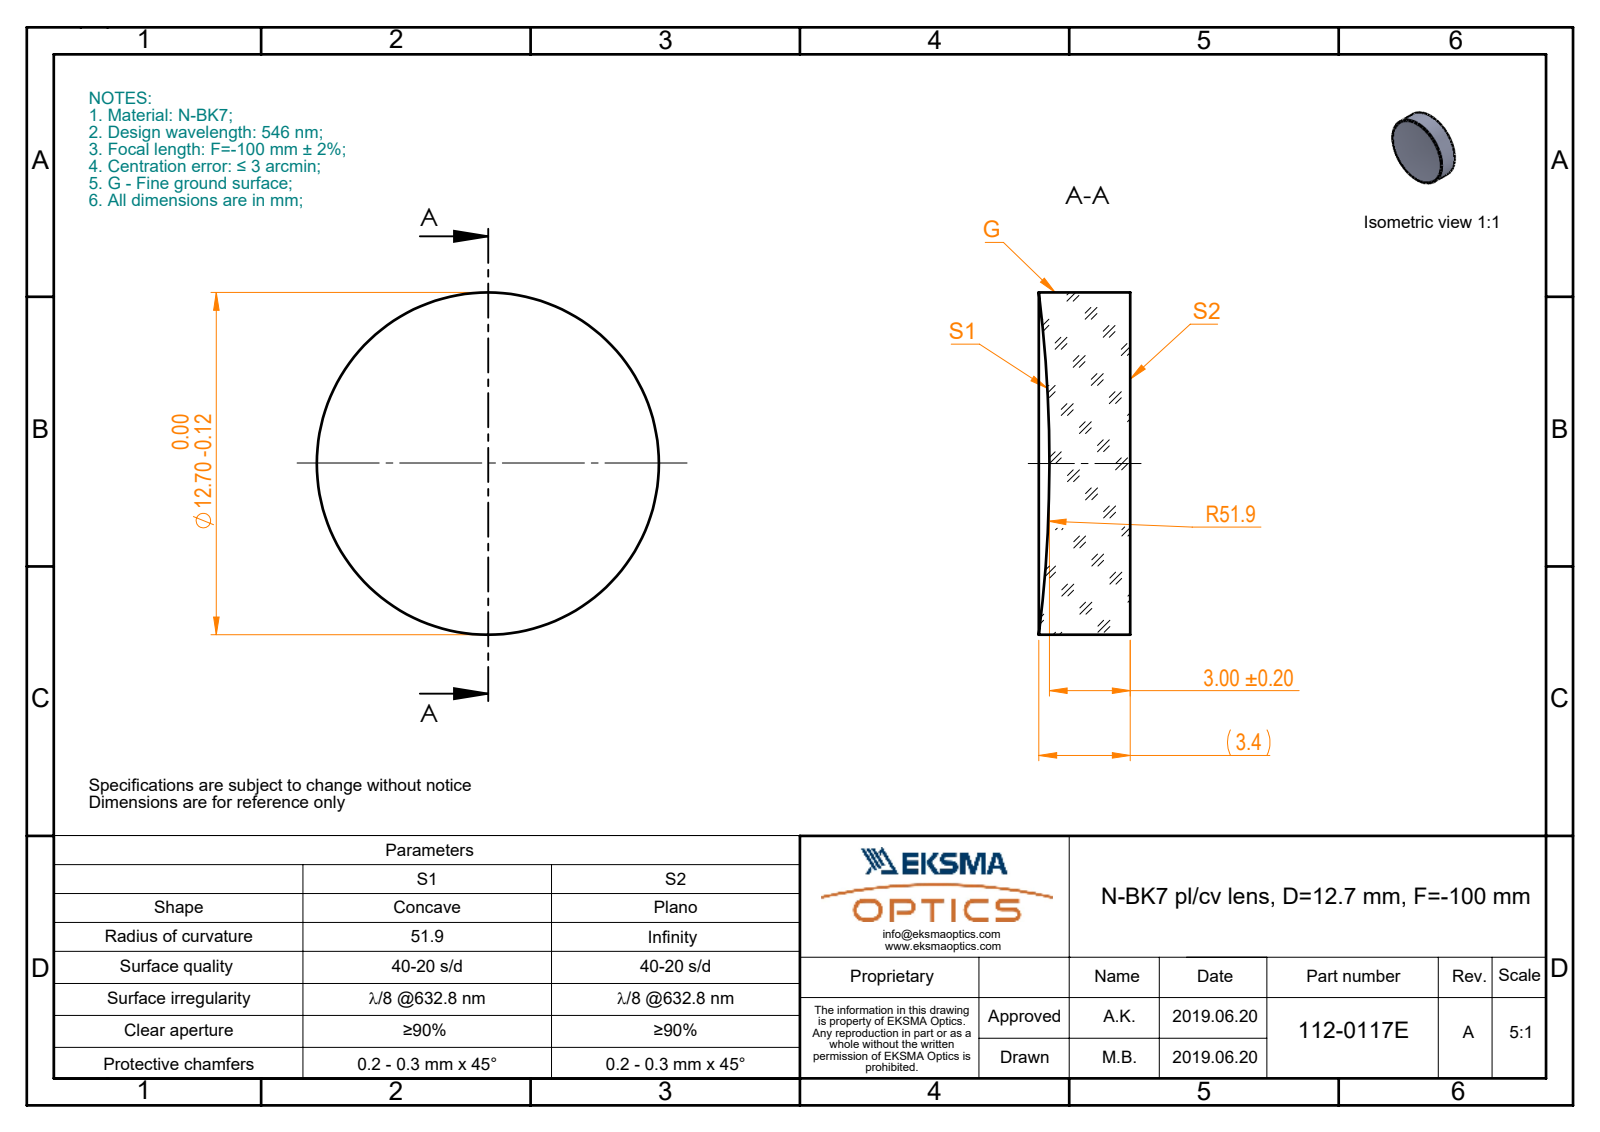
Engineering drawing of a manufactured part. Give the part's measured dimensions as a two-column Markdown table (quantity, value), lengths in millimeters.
| quantity | value |
| --- | --- |
| part name | 112-0117E BK7 pl-cv 12.7 F-100 |
| STEP written by | SolidWorks 2017 (CONFIG_CONTROL_DESIGN) |
| units | millimeters |
| bodies | 1 solid, 5 faces (1 planar, 2 cylindrical, 2 other) |
| overall size | 12.7 × 12.7 × 3.39 |
| volume | 405 mm³ |
| surface area | 389 mm² |
| round bosses / shafts (diameter × count) | 12.7 × 1 |
